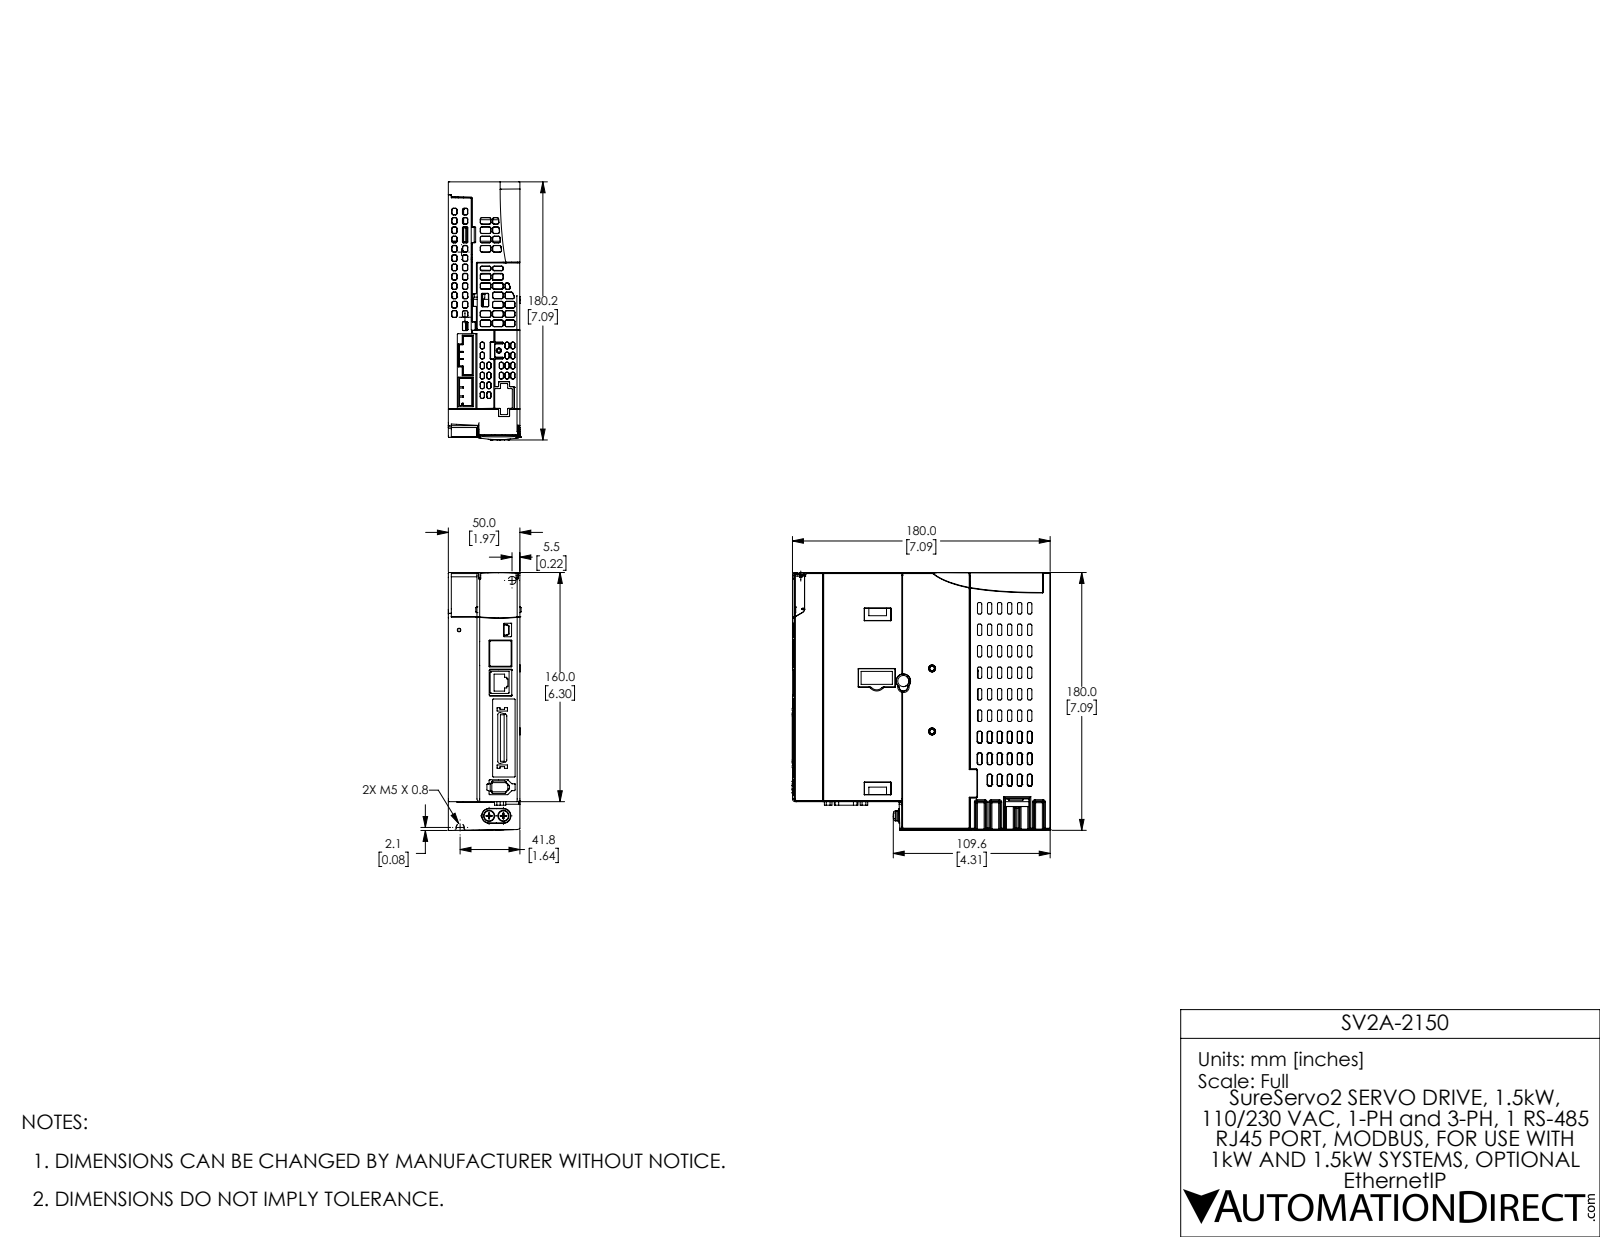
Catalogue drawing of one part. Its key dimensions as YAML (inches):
part_name: "SV2A-2075"
step_written_by: "SolidWorks 2017 (AUTOMOTIVE_DESIGN)"
units: inches
bodies: {solids: 4, faces: 4887, planar: 2217, cylindrical: 1151, other: 1519}
overall_size: [7.094, 7.091, 2]
volume: 66.33
surface_area: 291.7
round_holes:
  - {diameter: 0.044, count: 15}
  - {diameter: 0.118, count: 7}
  - {diameter: 0.02, count: 5}
  - {diameter: 0.067, count: 2}
  - {diameter: 0.177, count: 2}
  - {diameter: 0.197, count: 2}
  - {diameter: 0.059, count: 1}
  - {diameter: 0.071, count: 1}
  - {diameter: 0.308, count: 1}
round_bosses_or_shafts:
  - {diameter: 0.228, count: 3}
  - {diameter: 0.217, count: 3}
  - {diameter: 0.209, count: 3}
  - {diameter: 0.11, count: 3}
  - {diameter: 0.307, count: 2}
  - {diameter: 0.276, count: 2}
  - {diameter: 0.256, count: 2}
  - {diameter: 0.157, count: 2}
partial_cylinders:
  - {radius: 0.02, count: 234}
  - {radius: 0.012, count: 155}
  - {radius: 0.031, count: 55}
  - {radius: 0.008, count: 50}
  - {radius: 0.016, count: 33}
  - {radius: 0.039, count: 32}
  - {radius: 0.004, count: 31}
  - {radius: 0.03, count: 18}
face_to_face_distances: [1.969, 1.886, 1.882, 0.083, 0.075, 1.965, 0.079, 1.957, 1.89, 1.961]
hole_center_spacings: [0.09, 0.09, 0.156, 0.238, 0.18, 0.156, 0.18, 0.239]
